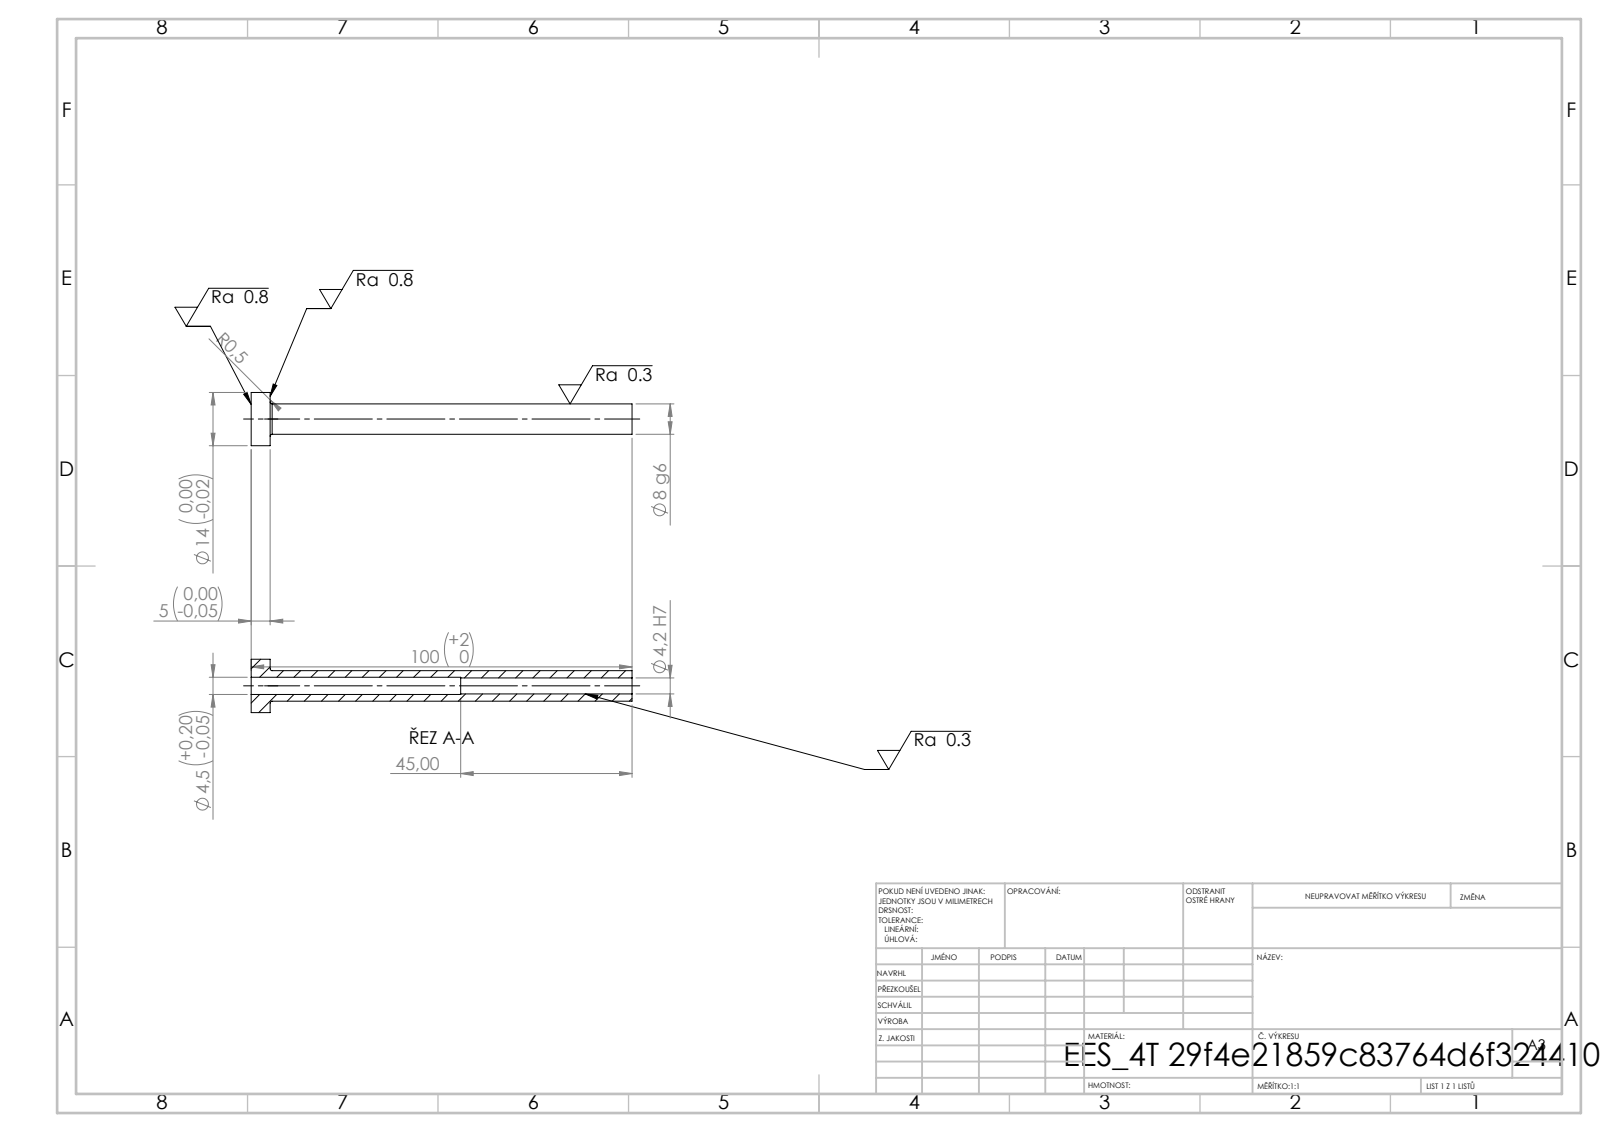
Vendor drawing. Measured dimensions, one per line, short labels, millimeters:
written by: SolidWorks 2019 (CONFIG_CONTROL_DESIGN)
unit: mm
bodies: 1 solid, 14 faces (4 planar, 8 cylindrical, 2 other)
size: 100 × 14 × 14
volume: 4 048 mm³; area: 4 254 mm²
holes: 1× ⌀4.2, 1× ⌀4.5
bosses: 1× ⌀14, 1× ⌀8
face distances: 5, 100, 95, 55, 50, 45
